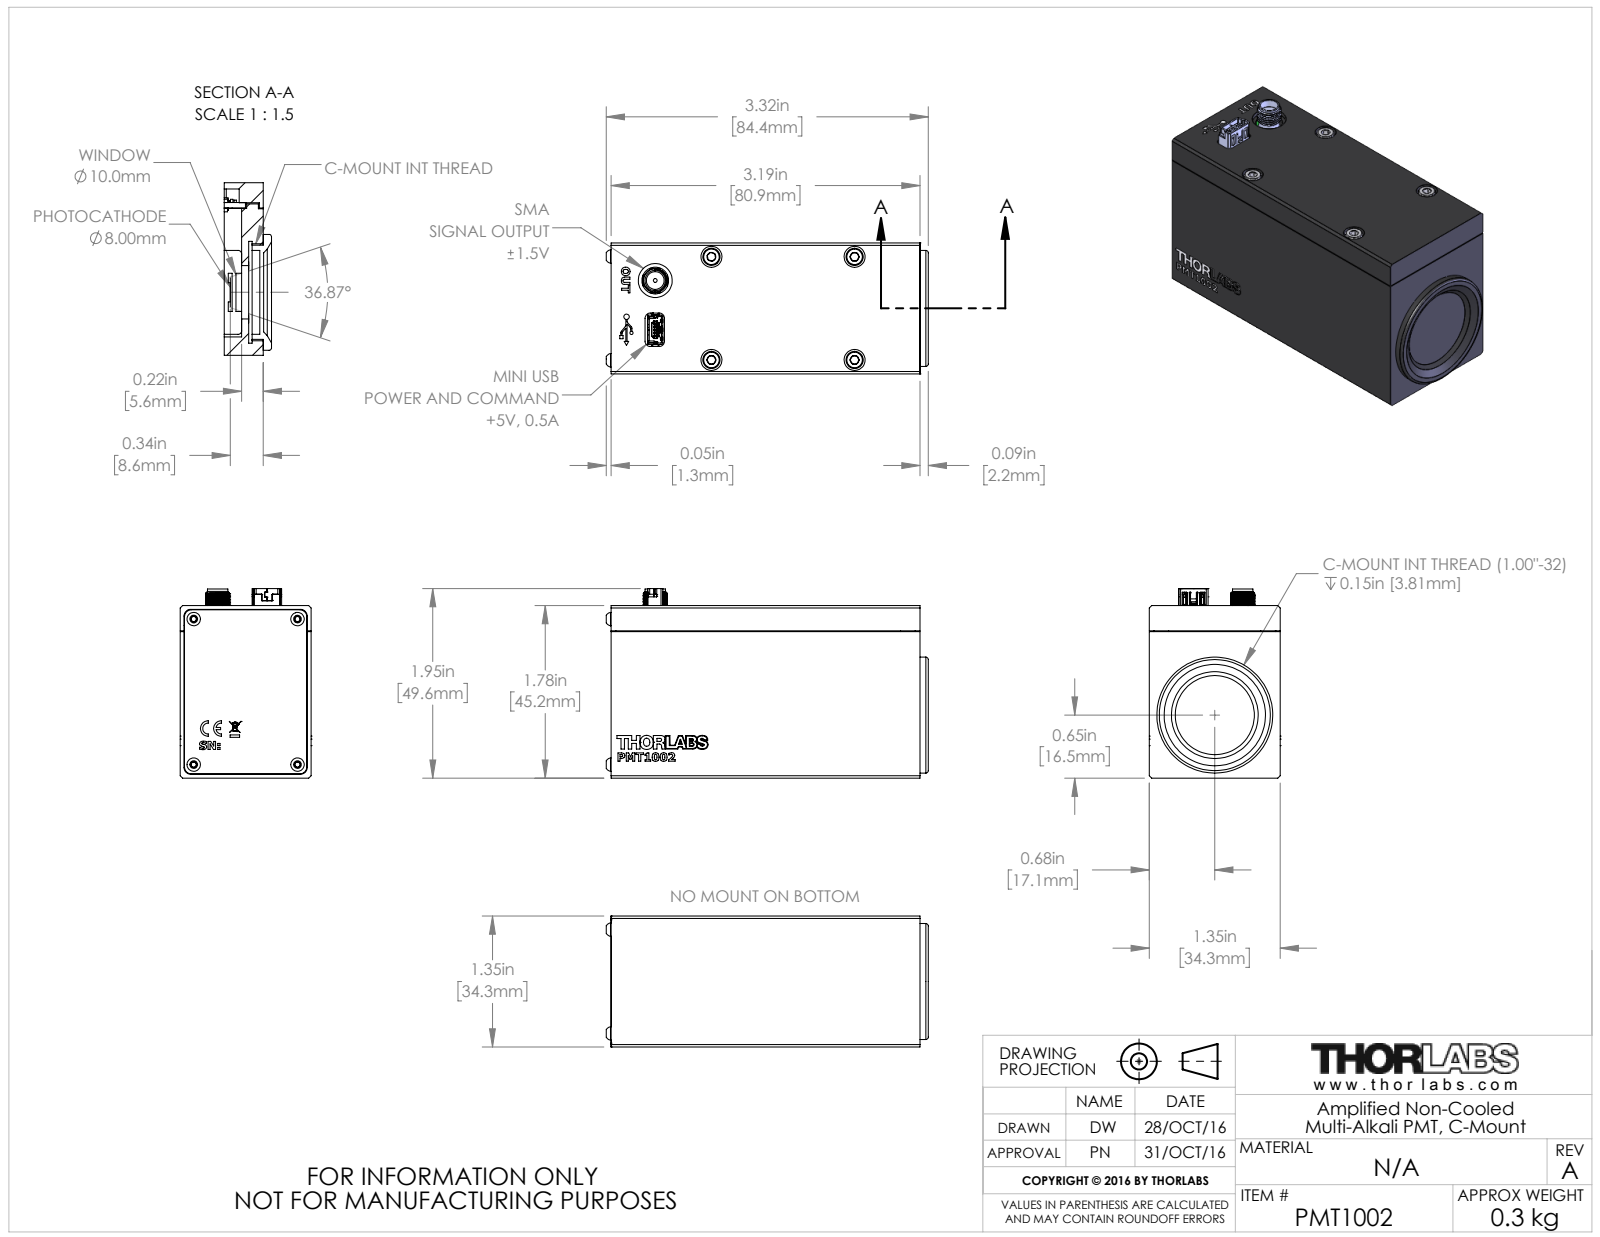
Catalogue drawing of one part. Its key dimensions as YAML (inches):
part_name: "TTN118002-E0W"
step_written_by: "SolidWorks 2016 (AUTOMOTIVE_DESIGN)"
units: inches
bodies: {solids: 0, faces: 458, planar: 246, cylindrical: 110, other: 102}
overall_size: [3.321, 1.955, 1.35]
round_holes:
  - {diameter: 0.217, count: 4}
  - {diameter: 0.033, count: 1}
  - {diameter: 0.055, count: 1}
  - {diameter: 0.183, count: 1}
  - {diameter: 0.275, count: 1}
  - {diameter: 0.35, count: 1}
round_bosses_or_shafts:
  - {diameter: 0.177, count: 4}
  - {diameter: 0.138, count: 4}
  - {diameter: 1.195, count: 1}
  - {diameter: 0.246, count: 1}
  - {diameter: 0.211, count: 1}
partial_cylinders:
  - {radius: 0.004, count: 12}
  - {radius: 0.02, count: 9}
  - {radius: 0.07, count: 8}
  - {radius: 0.055, count: 4}
  - {radius: 0.006, count: 3}
  - {radius: 0.006, count: 2}
  - {radius: 0.012, count: 2}
  - {radius: 0.056, count: 2}
face_to_face_distances: [1.35, 1.78, 1.577, 0.203, 3.185, 3.19, 1.511, 0.066, 0.269, 3.185]
hole_center_spacings: [1.063, 1.476, 1.819, 2.07, 2.213, 0.173, 0.476, 0.477]
